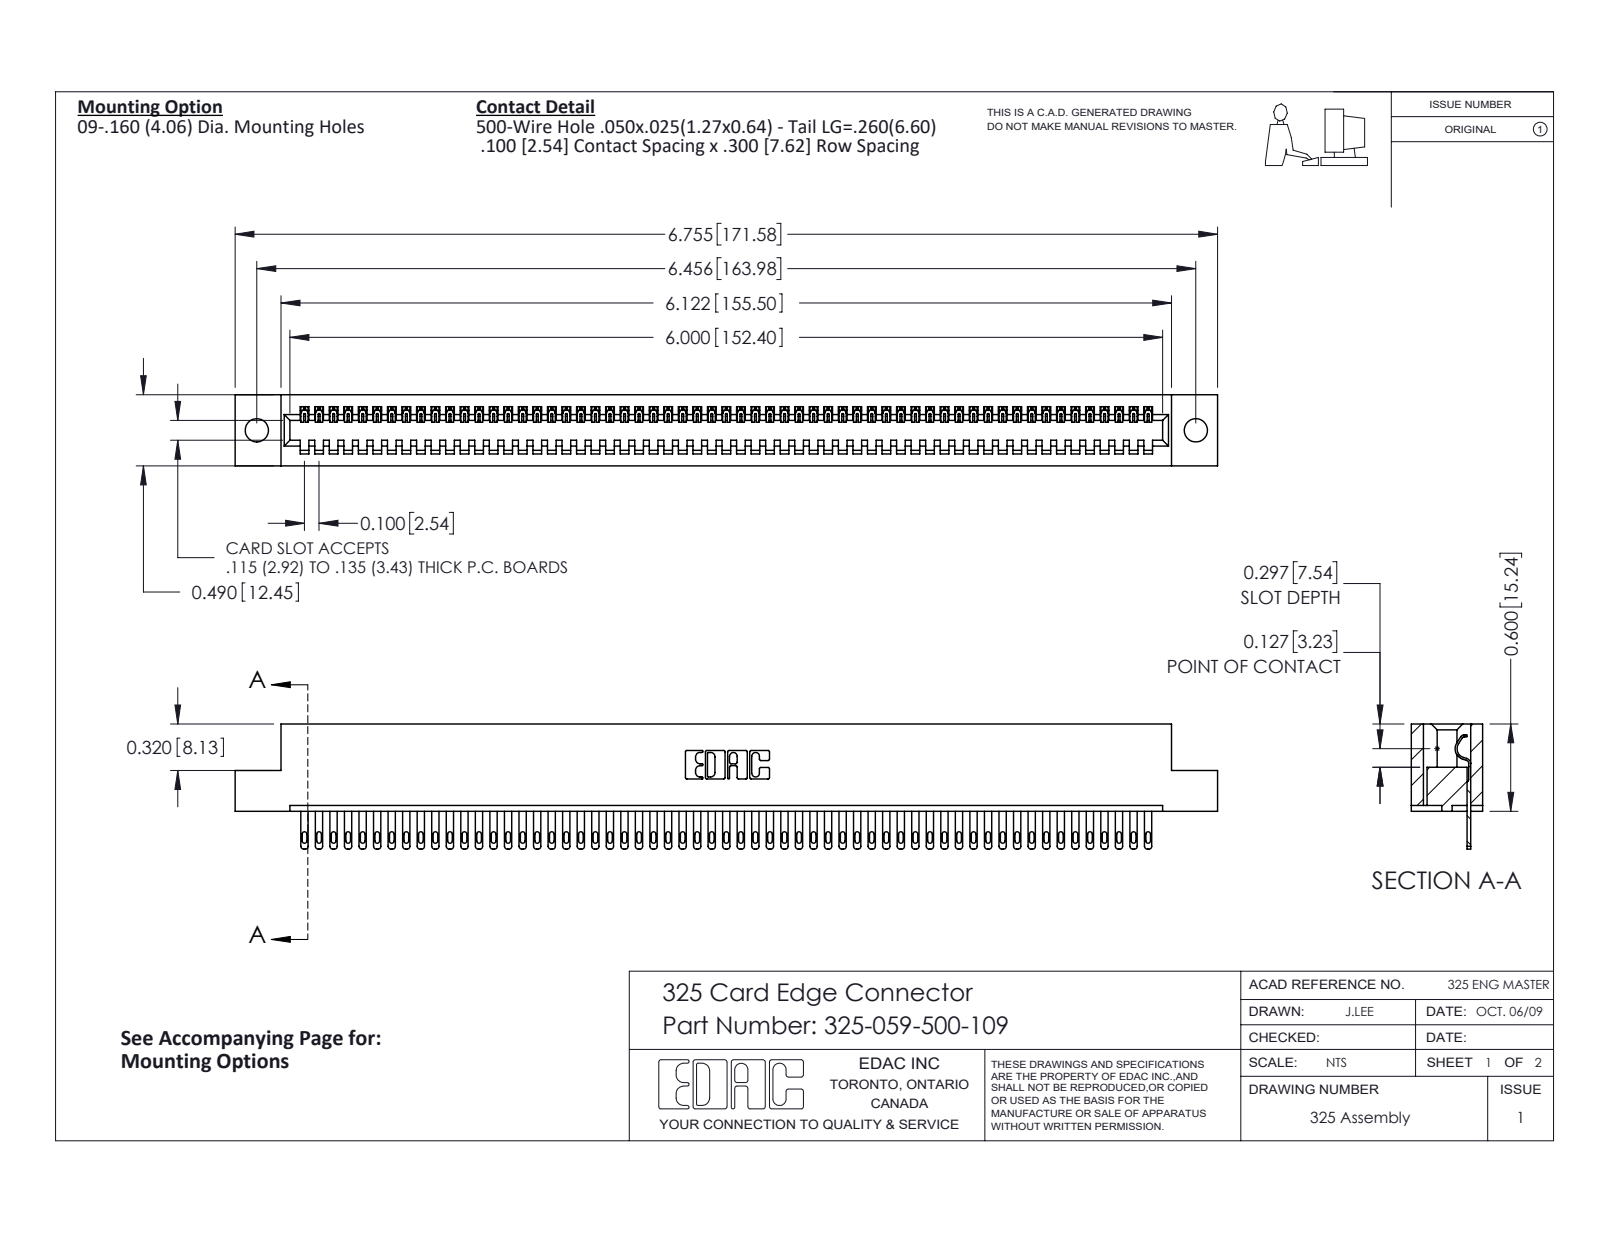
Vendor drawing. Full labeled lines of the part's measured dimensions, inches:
Part name (STEP PRODUCT): 325 Part_.160 TH; 325-059-500-109; 325-292-001_325-293-100
STEP written by: SolidWorks 2016 (CONFIG_CONTROL_DESIGN)
Units: inches
Bodies: 60 solids, 3300 faces (2194 planar, 1106 cylindrical, 0 other)
Overall size (bounding box): 6.755 × 0.86 × 0.49
Volume: 1.326 in³ · Surface area: 37.28 in²
Round holes (diameter × count): ⌀0.16 ×2
Partial cylindrical surfaces — rounded edges, fillets, slot ends (radius × count): R0.006 ×118, R0.016 ×118, R0.02 ×118, R0.01 ×22, R0.007 ×6, R0.031 ×6, R0.026 ×3, R0.014 ×1
Main face-to-face distances: 0.083, 0.407, 0.3, 0.49, 0.107, 0.383, 0.025, 0.325, 0.56, 0.263
Hole centre spacings: 6.456
